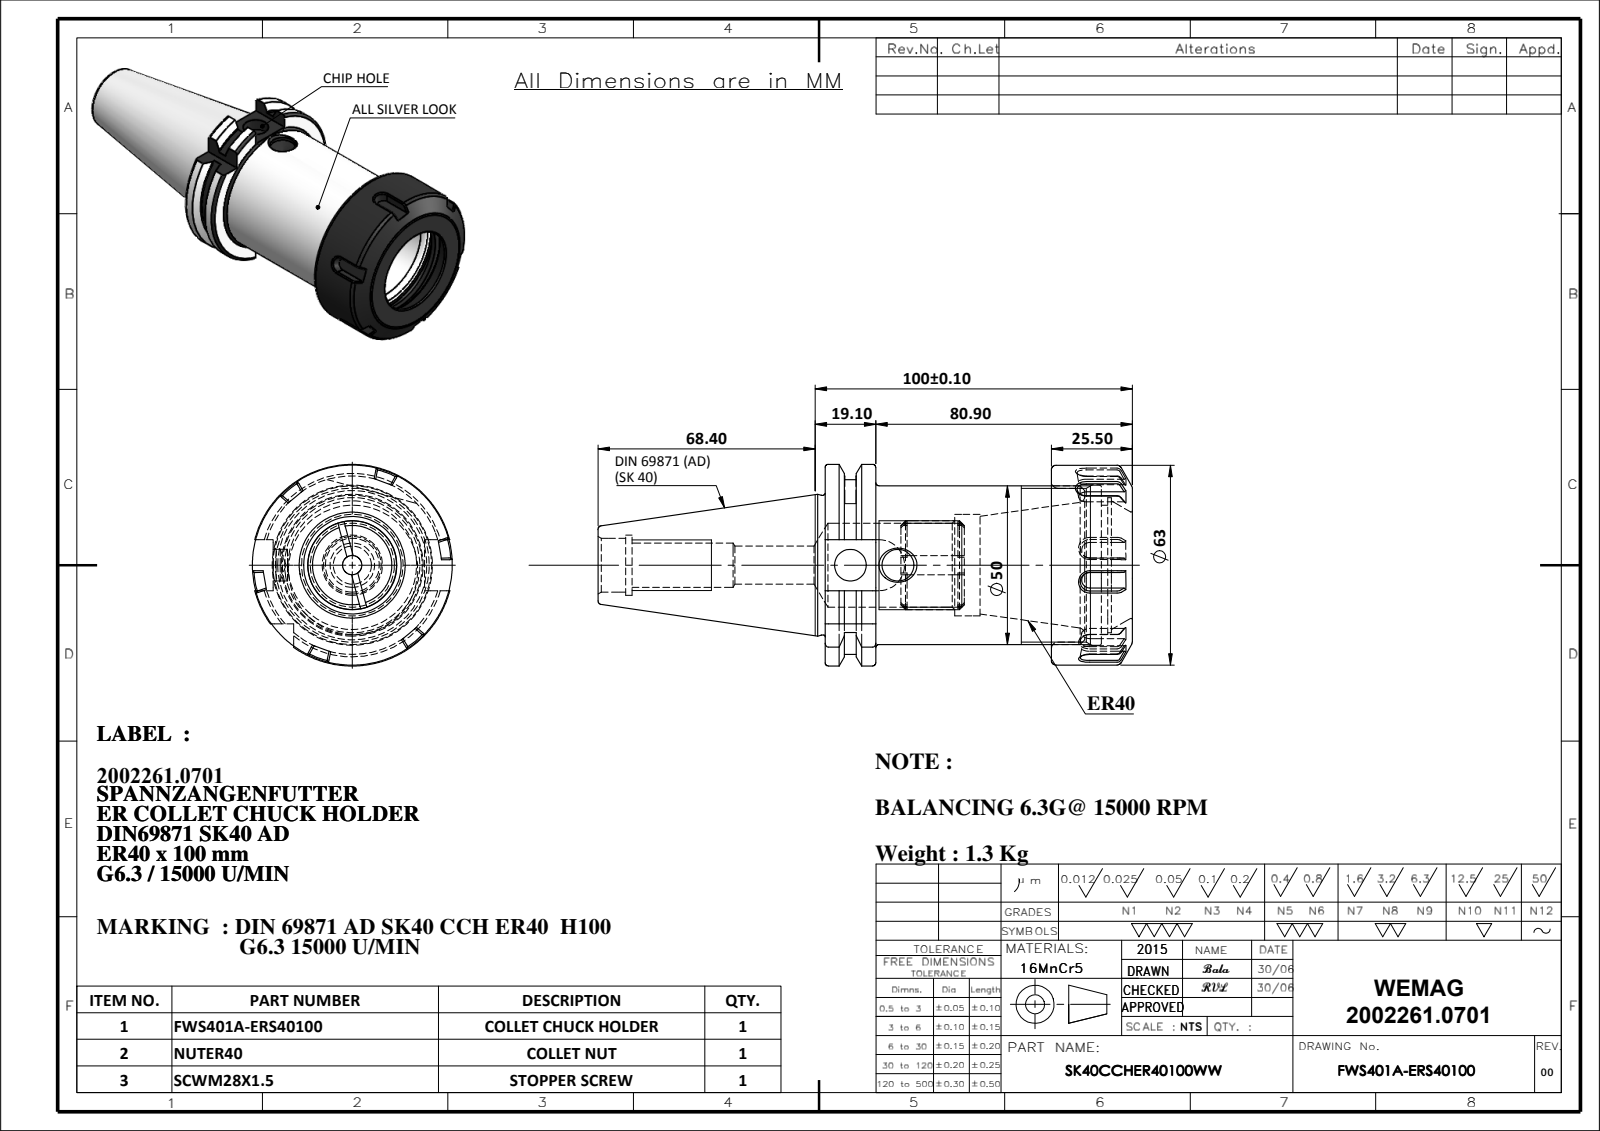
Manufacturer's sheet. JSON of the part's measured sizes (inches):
{"part_name": "SK40CCHER40100WW; FT NUT ER 40; FTSCWM28X150.; 91406-ER140100", "step_written_by": "SolidWorks 2018 (CONFIG_CONTROL_DESIGN)", "units": "inches", "bodies": {"solids": 3, "faces": 242, "planar": 79, "cylindrical": 48, "other": 115}, "overall_size": [6.63, 2.502, 2.48], "volume_in3": 13.11, "surface_area_in2": 82.88, "round_holes": [[0.394, 2], [0.236, 1], [0.472, 1], [0.551, 1], [0.669, 1], [0.748, 1], [1.043, 1], [1.26, 1], [1.604, 1], [1.677, 1], [1.909, 1], [1.988, 1]], "round_bosses_or_shafts": [[2.48, 1], [1.969, 1], [1.734, 1], [1.102, 1]], "partial_cylinders_radius": [[0.317, 1], [1.107, 1], [1.251, 1]], "face_to_face_distances": [3.811, 0.626, 3.185, 2.807, 2.181, 1.004, 3.425, 2.799, 0.618, 0.386], "hole_center_spacings": [0.059, 0.591]}
